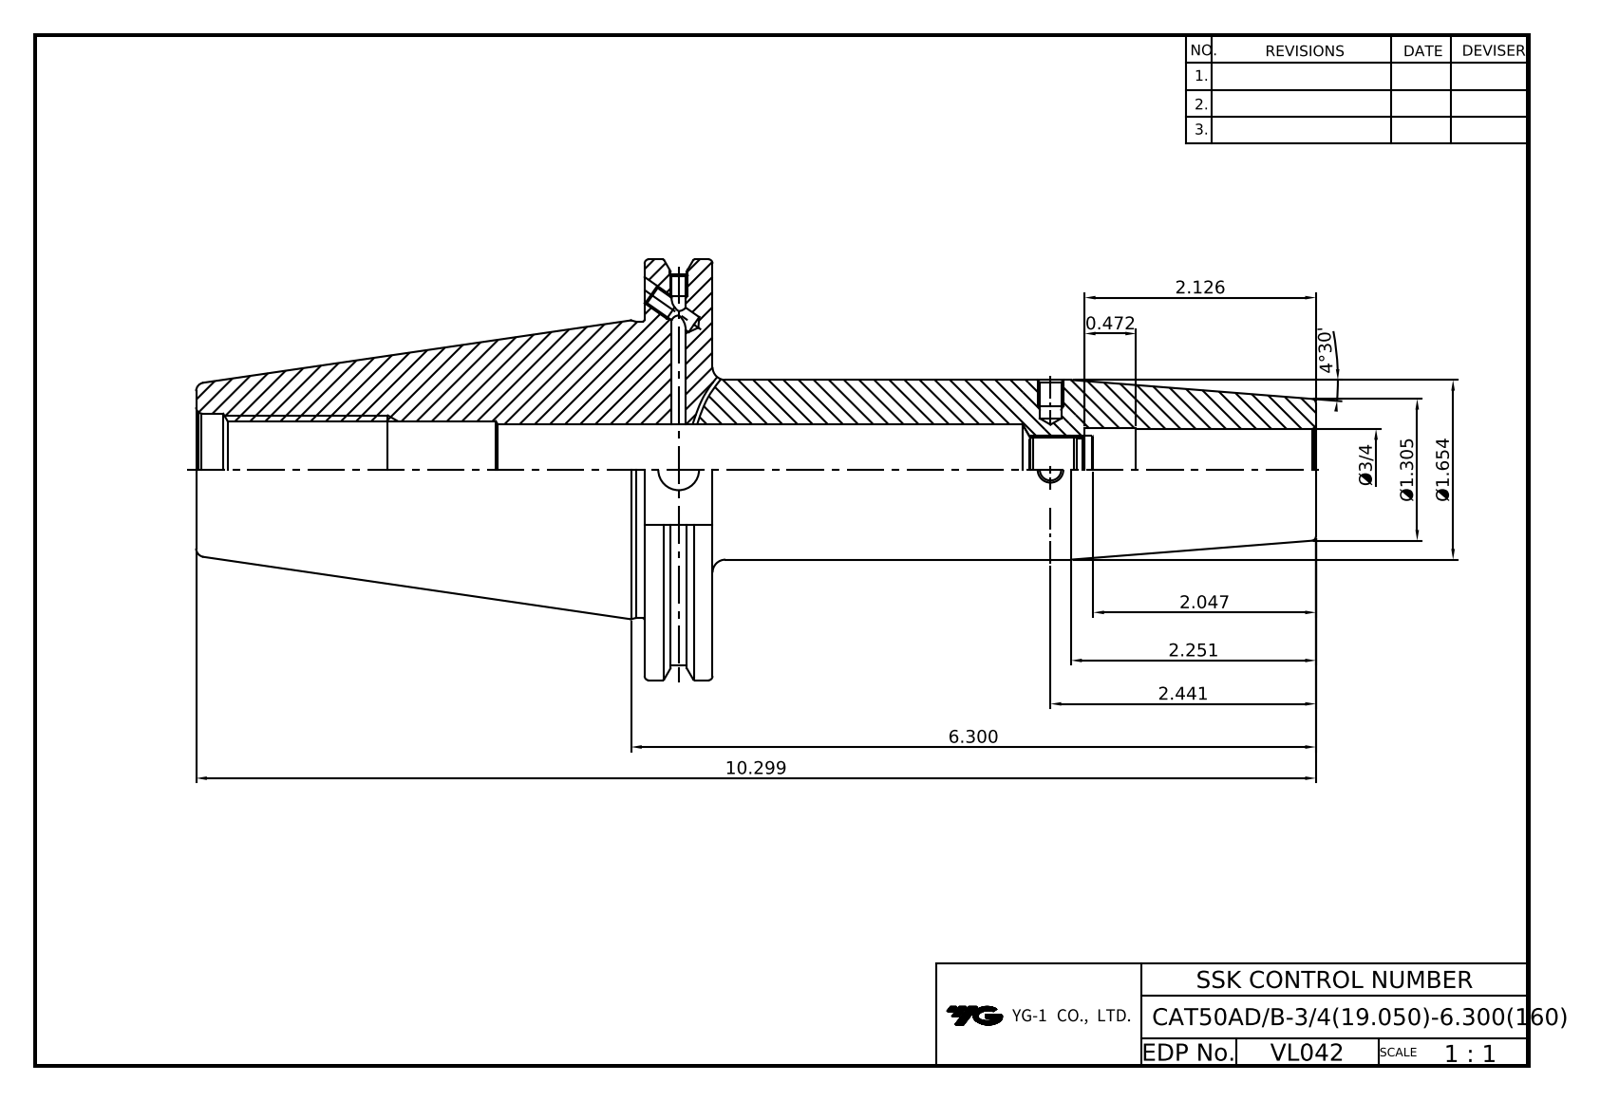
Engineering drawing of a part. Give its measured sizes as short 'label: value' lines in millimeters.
name: LO-CAT50ADB-SFH19.05-160
written by: Autodesk Inventor 2025 (AUTOMOTIVE_DESIGN)
unit: mm
bodies: 1 solid, 84 faces (37 planar, 26 cylindrical, 21 other)
size: 261.6 × 98.42 × 94.69
volume: 456 289 mm³; area: 70 591 mm²
holes: 2× ⌀3.24, 2× ⌀4.13, 2× ⌀4.2, 2× ⌀5, 1× ⌀9.53, 1× ⌀14.92, 1× ⌀19.05, 1× ⌀20.25, 1× ⌀21.97, 1× ⌀26.2
bosses: 1× ⌀98.42, 1× ⌀91.29, 1× ⌀69.25, 1× ⌀42
face distances: 15.88, 104.77, 120.65, 261.6, 156.83, 140.95, 73.03, 25.9, 110.82, 6.05
